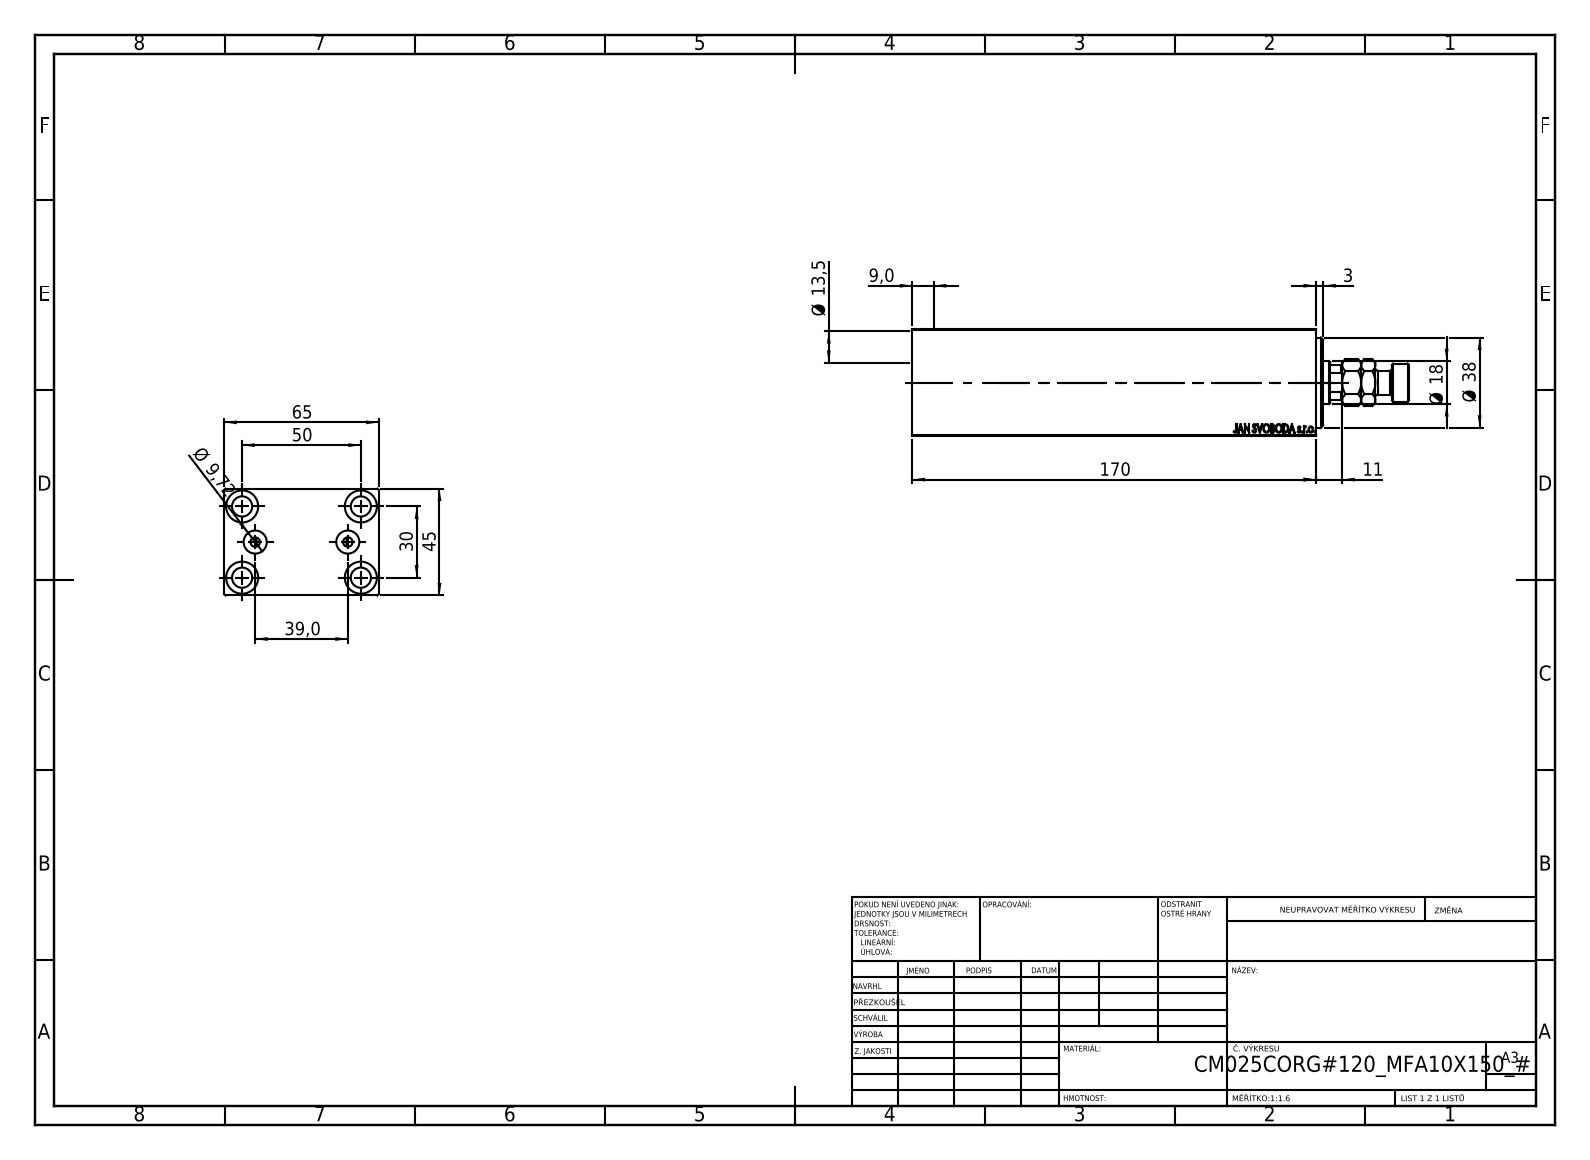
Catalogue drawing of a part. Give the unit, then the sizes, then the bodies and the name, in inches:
Units: inches
Overall size (bounding box): 8.228 × 2.559 × 1.772
Round holes (diameter × count): ⌀0.335 ×5, ⌀0.531 ×4, ⌀0.157 ×2, ⌀0.383 ×2, ⌀0.709 ×1, ⌀0.846 ×1, ⌀0.984 ×1, ⌀1.063 ×1, ⌀1.496 ×1
Round bosses / shafts (diameter × count): ⌀0.63 ×1, ⌀0.394 ×1
Partial cylindrical surfaces — rounded edges, fillets, slot ends (radius × count): R0.335 ×1
Main face-to-face distances: 1.772, 2.559, 0.236, 6.26, 6.457, 6.693, 6.496, 0.197, 0.118, 0.315
Hole centre spacings: 0.629, 1.148, 1.849, 0.768, 1.181, 1.969, 2.296, 1.535
Volume: 26.12 in³ · Surface area: 151.2 in²
Bodies: 4 solids, 910 faces (424 planar, 60 cylindrical, 426 other)
Part name (STEP PRODUCT): V450CM_C_VCP; V450CM_VC_B; V450CM_C_Body; MFA
STEP written by: SolidWorks 2019 (CONFIG_CONTROL_DESIGN)
